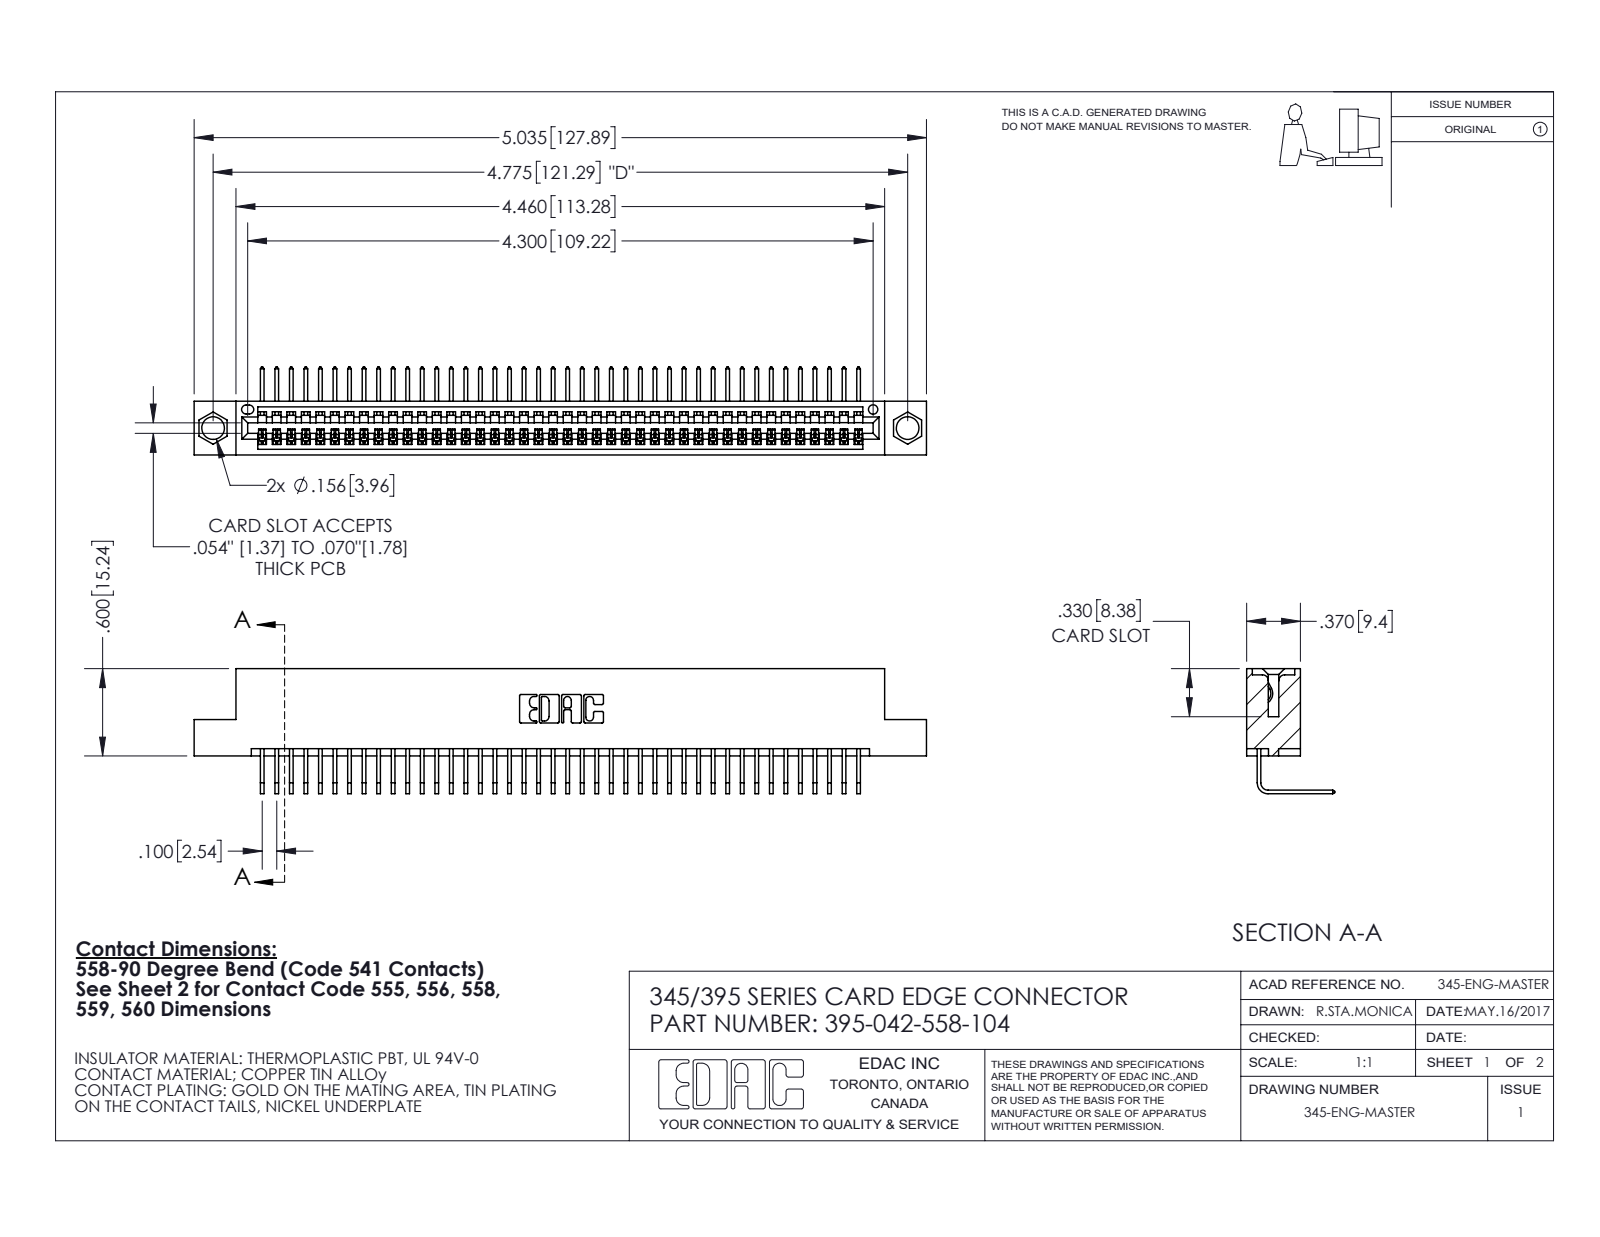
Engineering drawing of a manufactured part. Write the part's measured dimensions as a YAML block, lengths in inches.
part_name: "345-292-001_558 Tail - 2; 395-042-558-104; 345 Part_Flush Mounting Lugs - 0.156 Dia-TI"
step_written_by: "SolidWorks 2020 (CONFIG_CONTROL_DESIGN)"
units: inches
bodies: {solids: 43, faces: 2660, planar: 1858, cylindrical: 802, other: 0}
overall_size: [5.035, 0.859, 0.605]
volume: 0.743
surface_area: 26.12
round_holes:
  - {diameter: 0.156, count: 2}
  - {diameter: 0.064, count: 1}
partial_cylinders:
  - {radius: 0.006, count: 84}
  - {radius: 0.01, count: 22}
  - {radius: 0.007, count: 6}
  - {radius: 0.031, count: 6}
  - {radius: 0.026, count: 3}
  - {radius: 0.031, count: 2}
  - {radius: 0.04, count: 2}
  - {radius: 0.014, count: 1}
face_to_face_distances: [0.072, 0.298, 0.37, 0.2, 0.098, 0.272, 0.025, 0.225, 0.149, 0.072]
hole_center_spacings: [0.27, 4.539, 4.775]
